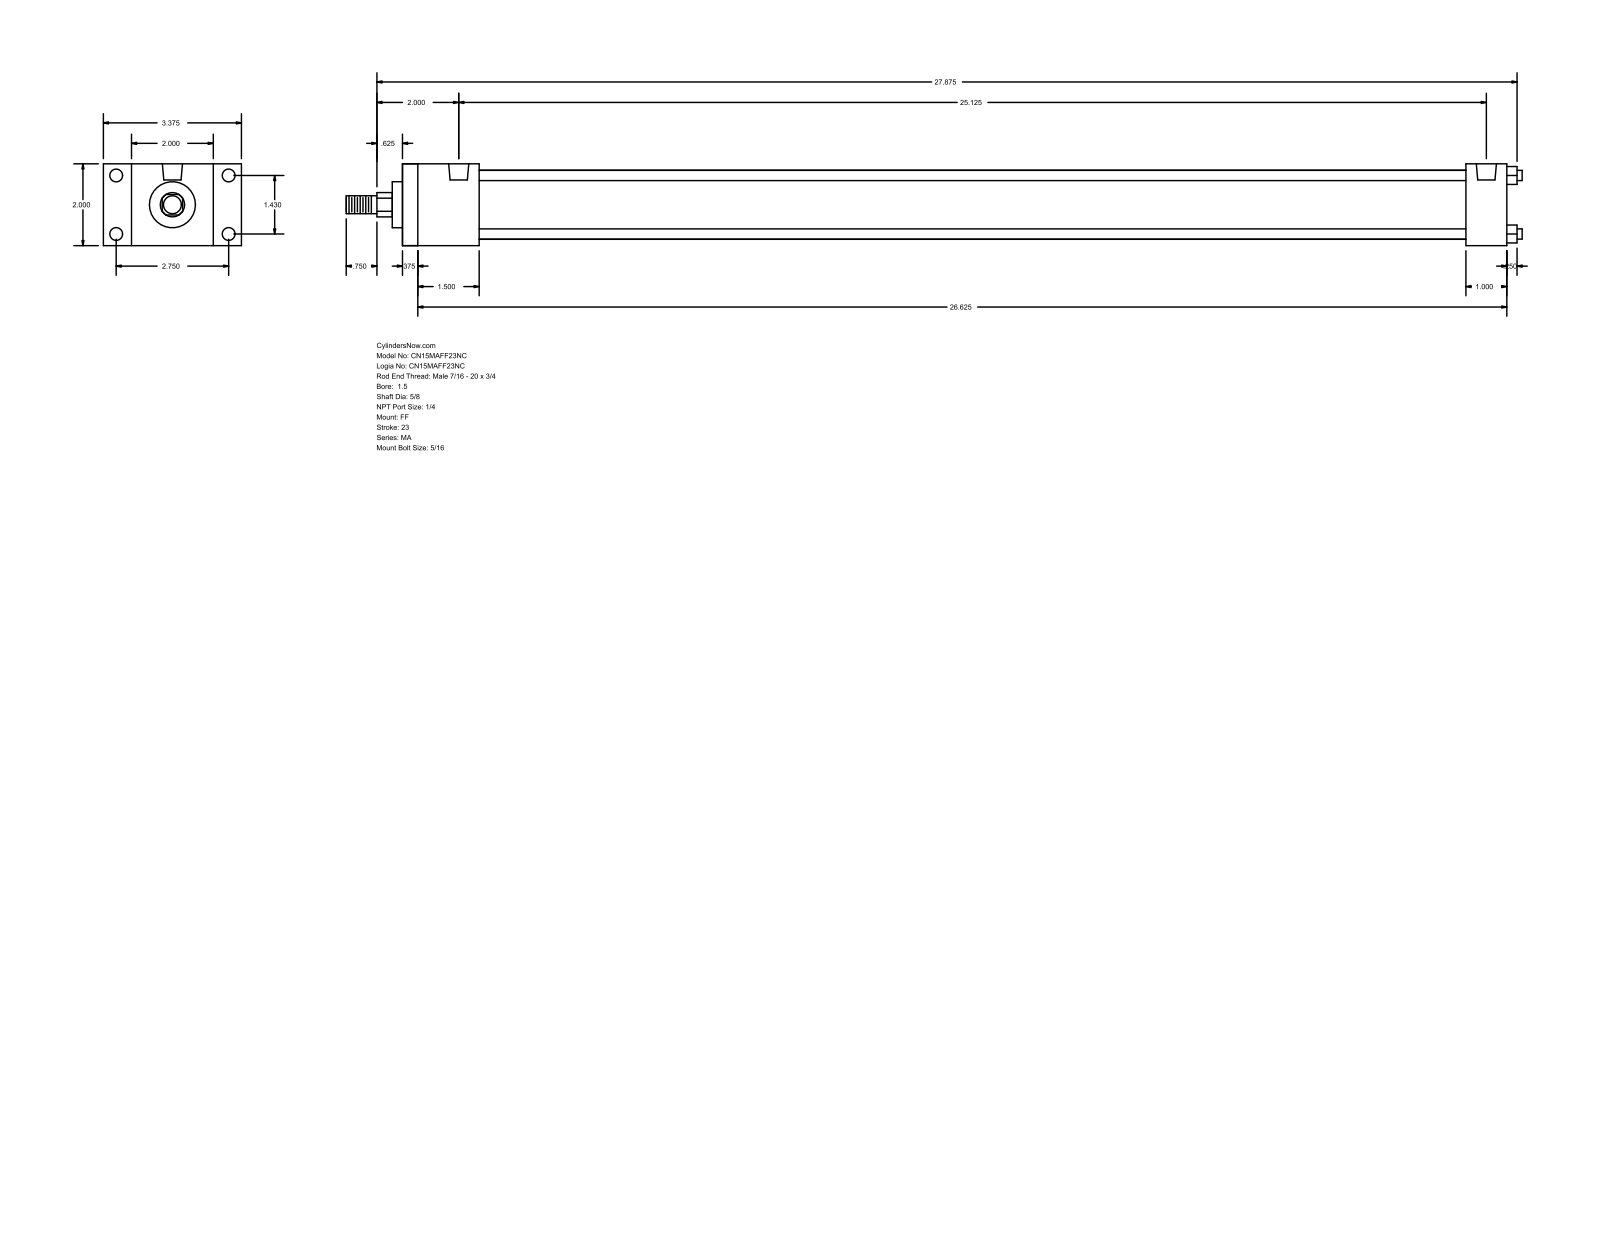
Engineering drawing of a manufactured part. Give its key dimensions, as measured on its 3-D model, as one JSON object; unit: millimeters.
{"part_name": "MA_FF__0150_0.625", "step_written_by": "GSSL Pune (CONFIG_CONTROL_DESIGN)", "units": "millimeters", "bodies": {"solids": 0, "faces": 92, "planar": 64, "cylindrical": 28, "other": 0}, "overall_size": [730.25, 85.72, 50.8], "round_holes": [[7.94, 8], [12.49, 2]], "round_bosses_or_shafts": [[6.35, 4], [42.93, 1], [28.57, 1], [15.88, 1], [11.11, 1]], "partial_cylinders_radius": [[7.54, 1]], "face_to_face_distances": [50.8, 685.79, 676.27, 9.52, 25.4, 47.62, 660.39, 38.1, 650.87, 612.77], "hole_center_spacings": [36.32, 69.84, 78.72, 638.18]}
